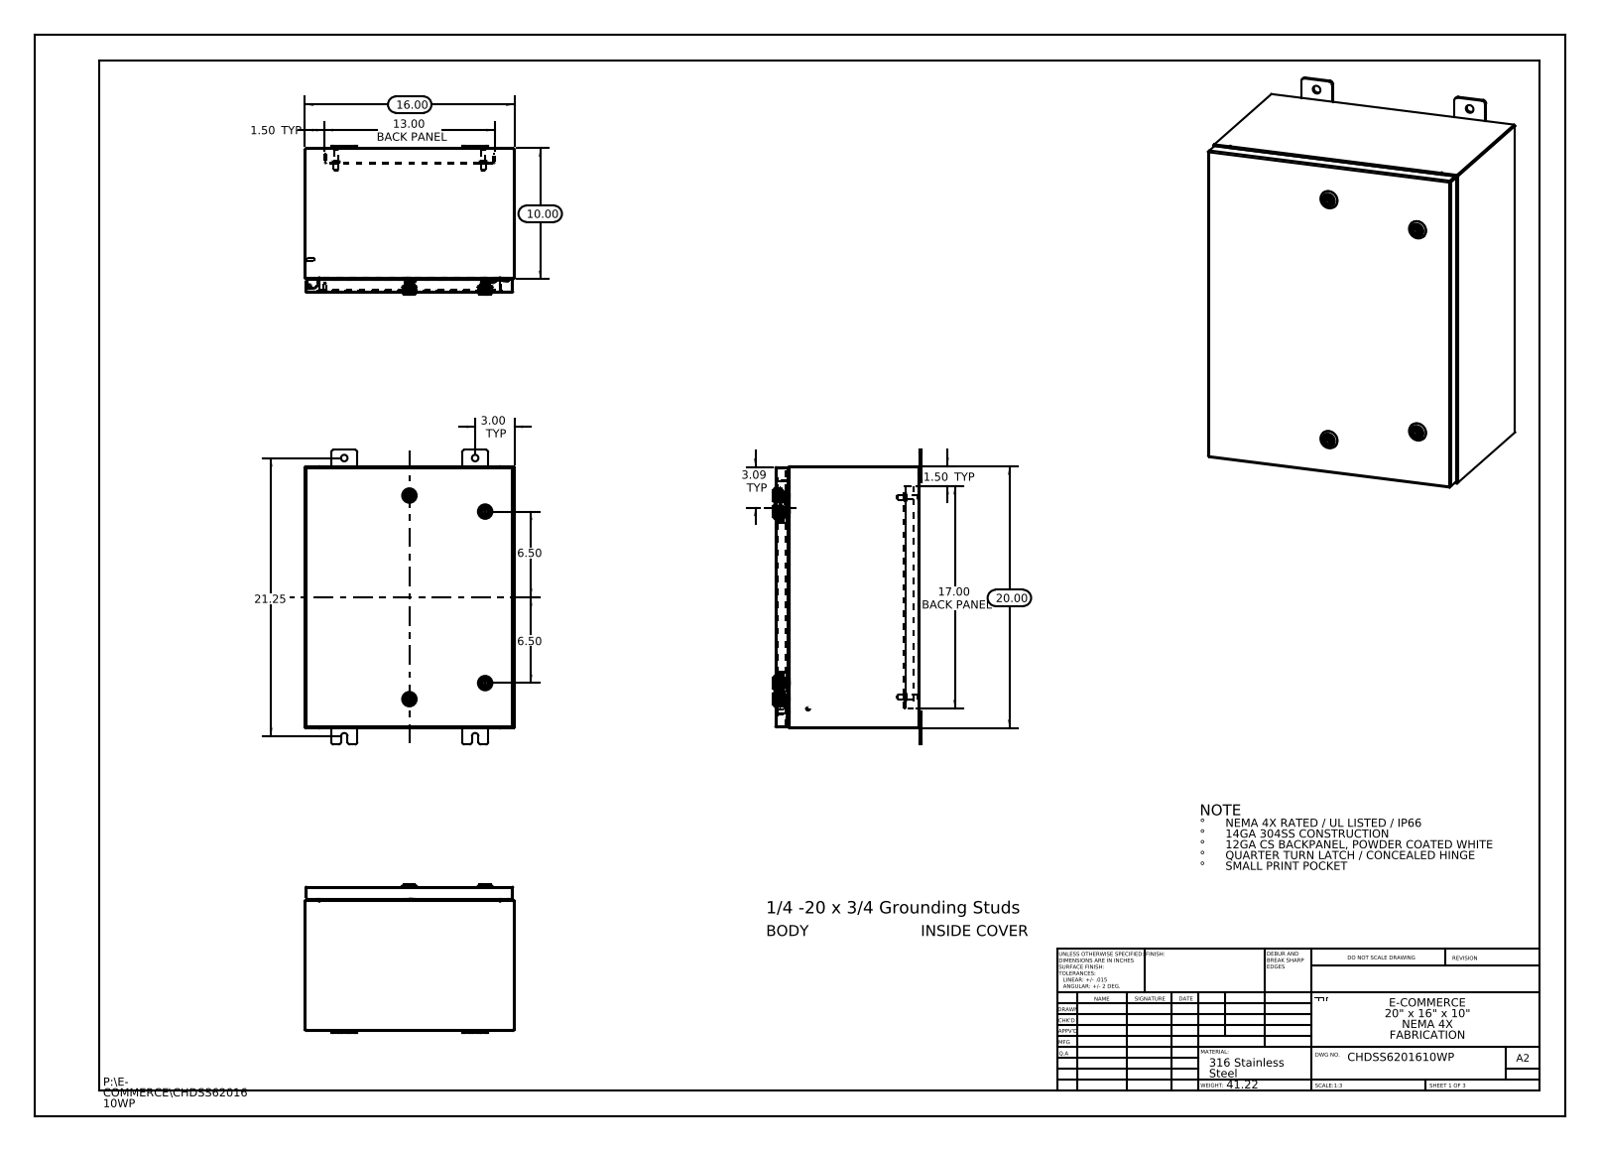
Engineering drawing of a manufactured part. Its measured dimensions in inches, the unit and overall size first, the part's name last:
Units: inches
Overall size (bounding box): 22.5 × 16 × 11.356
Round holes (diameter × count): ⌀0.5 ×8, ⌀0.136 ×4, ⌀0.197 ×4, ⌀0.394 ×4, ⌀0.4 ×4, ⌀0.63 ×4, ⌀0.787 ×4, ⌀0.211 ×1
Round bosses / shafts (diameter × count): ⌀0.236 ×6, ⌀1.102 ×4, ⌀0.78 ×4, ⌀0.626 ×4, ⌀0.625 ×4, ⌀0.61 ×4, ⌀0.531 ×4, ⌀0.392 ×4
Partial cylindrical surfaces — rounded edges, fillets, slot ends (radius × count): R0.006 ×132, R0.118 ×132, R0.028 ×48, R0.19 ×24, R0.013 ×20, R0.088 ×18, R0.02 ×16, R0.197 ×16
Main face-to-face distances: 0.075, 15.925, 0.074, 19.925, 11.01, 10.935, 10.936, 10.861, 0.104, 1
Hole centre spacings: 1.858, 3.065, 5.916, 10, 11.25, 15.25, 17.011, 18.261
Volume: 147 in³ · Surface area: 3 713 in²
Bodies: 43 solids, 3794 faces (1164 planar, 1186 cylindrical, 1444 other)
Part name (STEP PRODUCT): HW-CLH-E5-8004_Cam-232112-U-Industrilas; CHDSS6201610WP Top; Concealed Hinge (Cover Side); HW-CLH-R001-0500_2412-026240-2445-Industrilas (+8 more)
STEP written by: SolidWorks 2013 (CONFIG_CONTROL_DESIGN)
